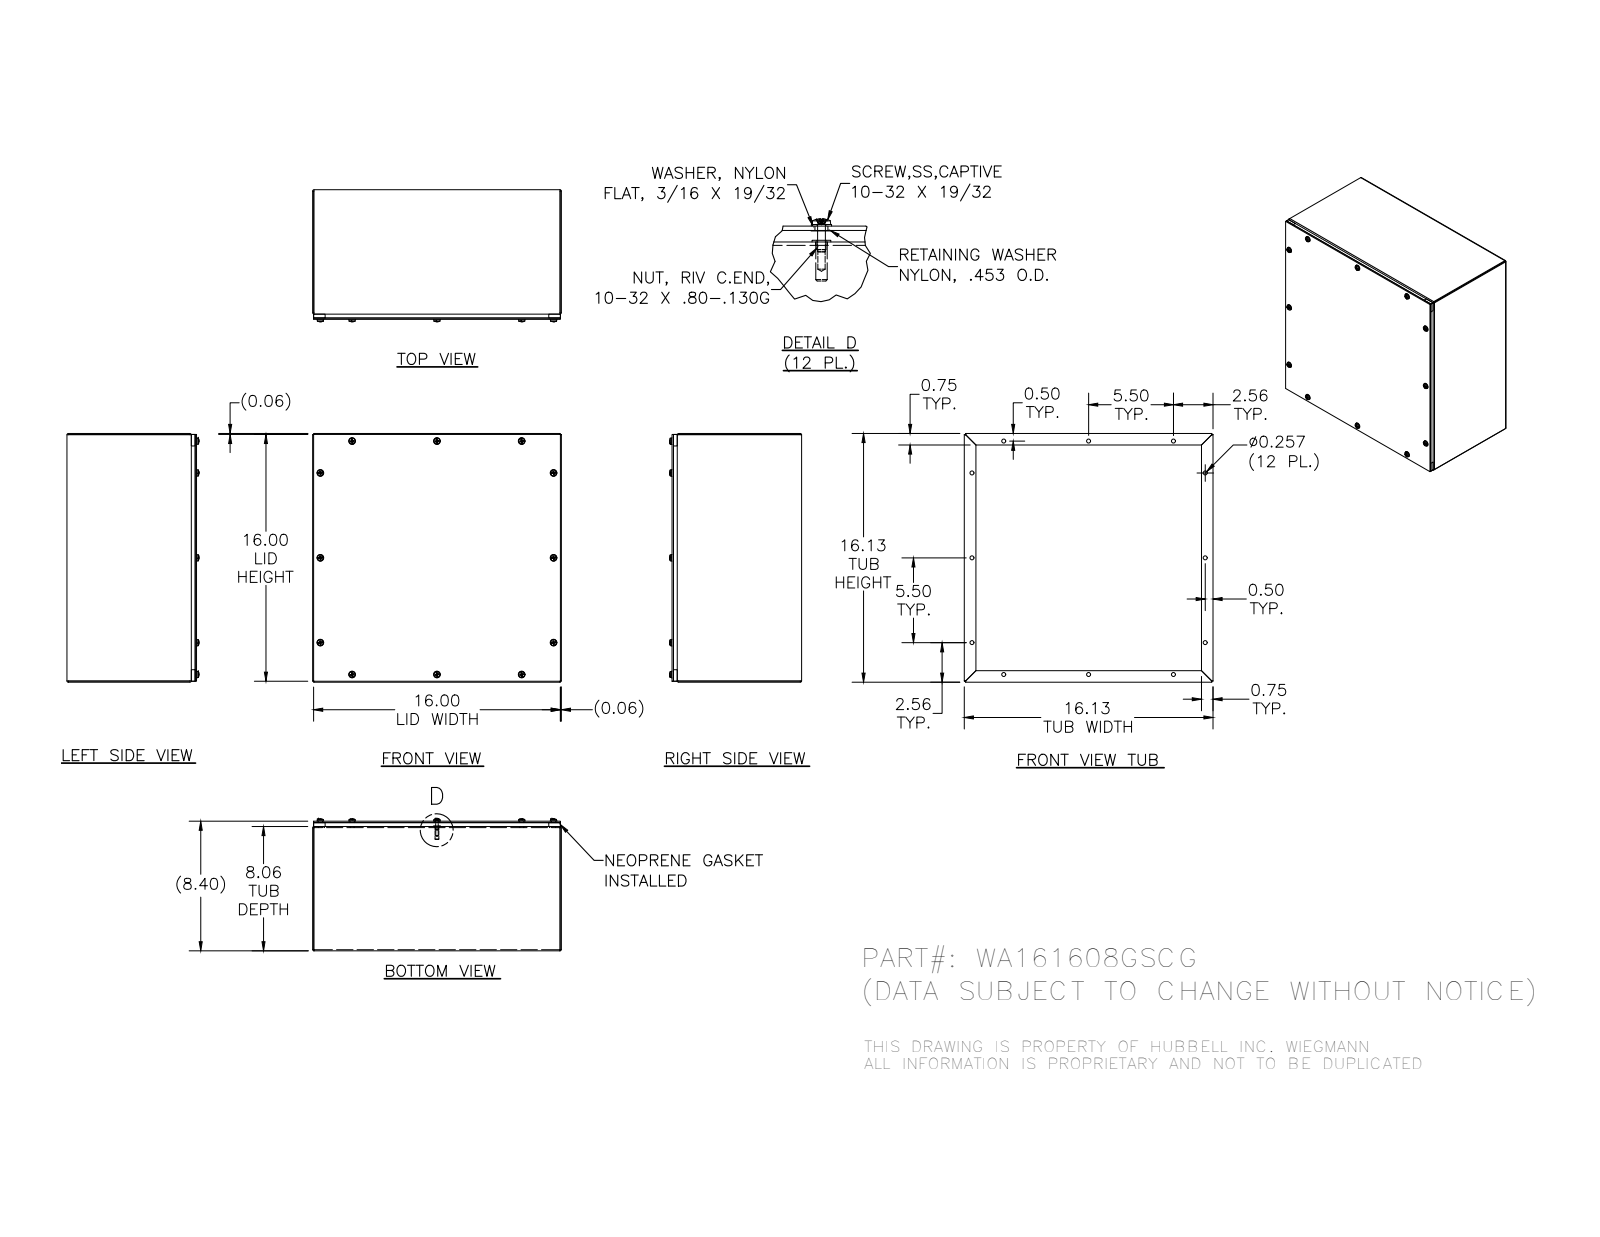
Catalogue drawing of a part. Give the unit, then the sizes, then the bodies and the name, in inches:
Units: inches
Overall size (bounding box): 16.125 × 16.125 × 8.558
Round holes (diameter × count): ⌀0.156 ×12, ⌀0.188 ×12, ⌀0.196 ×12, ⌀0.257 ×12, ⌀0.278 ×12, ⌀0.281 ×12
Round bosses / shafts (diameter × count): ⌀0.453 ×12, ⌀0.437 ×12, ⌀0.406 ×12, ⌀0.248 ×12, ⌀0.167 ×12
Partial cylindrical surfaces — rounded edges, fillets, slot ends (radius × count): R0.089 ×12, R0.016 ×8, R0.09 ×8
Main face-to-face distances: 0.074, 0.094, 8.33, 8.404, 8.236, 8.31, 0.074, 16.051, 15.977, 16.125
Hole centre spacings: 5.5, 16.094, 11, 15.093, 15.125, 13.224, 7.838, 7.839
Volume: 96.45 in³ · Surface area: 2 305 in²
Bodies: 54 solids, 1264 faces (596 planar, 328 cylindrical, 340 other)
Part name (STEP PRODUCT): 37210; 39035; WA1616GSCGLP; 34984 (+3 more)
STEP written by: SolidWorks 2014 (AUTOMOTIVE_DESIGN)
